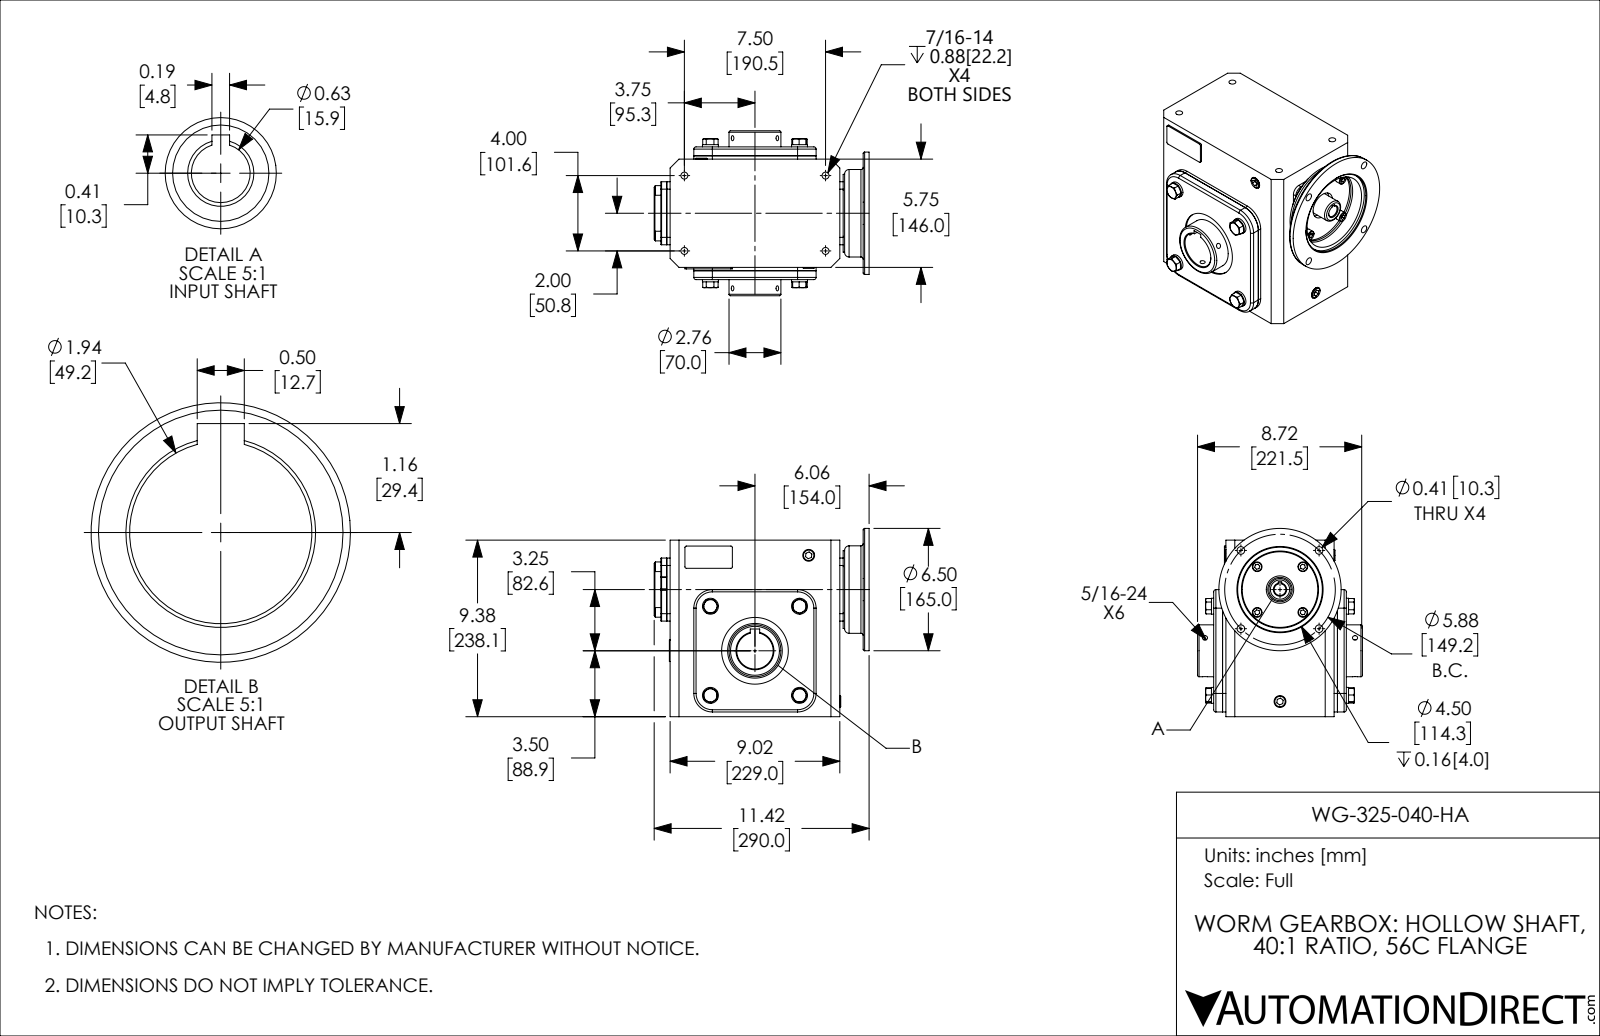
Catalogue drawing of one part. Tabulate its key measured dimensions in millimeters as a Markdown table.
| quantity | value |
| --- | --- |
| part name | WG-325-040-HA |
| STEP written by | SolidWorks 2017 (AUTOMOTIVE_DESIGN) |
| units | millimeters |
| bodies | 39 solids, 587 faces (314 planar, 178 cylindrical, 95 other) |
| overall size | 290 × 253.9 × 222.5 |
| volume | 8 452 000 mm³ |
| surface area | 633 600 mm² |
| round holes (diameter × count) | 6.9 × 6, 9.3 × 4, 10.3 × 4, 16 × 3, 15 × 1, 15.9 × 1, 24.8 × 1, 30 × 1, 37 × 1, 49.2 × 1, 62 × 1, 70 × 1 |
| round bosses / shafts (diameter × count) | 21.5 × 4, 13 × 4, 165 × 1, 118 × 1, 105 × 1, 72 × 1, 29 × 1 |
| partial cylindrical surfaces (radius × count) | 3 × 8, 2 × 7, 10 × 4, 23 × 4, 25 × 4, 0.5 × 2, 1 × 2 |
| main face-to-face distances | 2, 4.5, 165, 10, 14.5, 160.5, 150.5, 162.5, 177, 12 |
| hole center spacings | 74.6, 105.5, 107.8, 179.4, 202.5, 60.6, 101.6, 111.5 |
